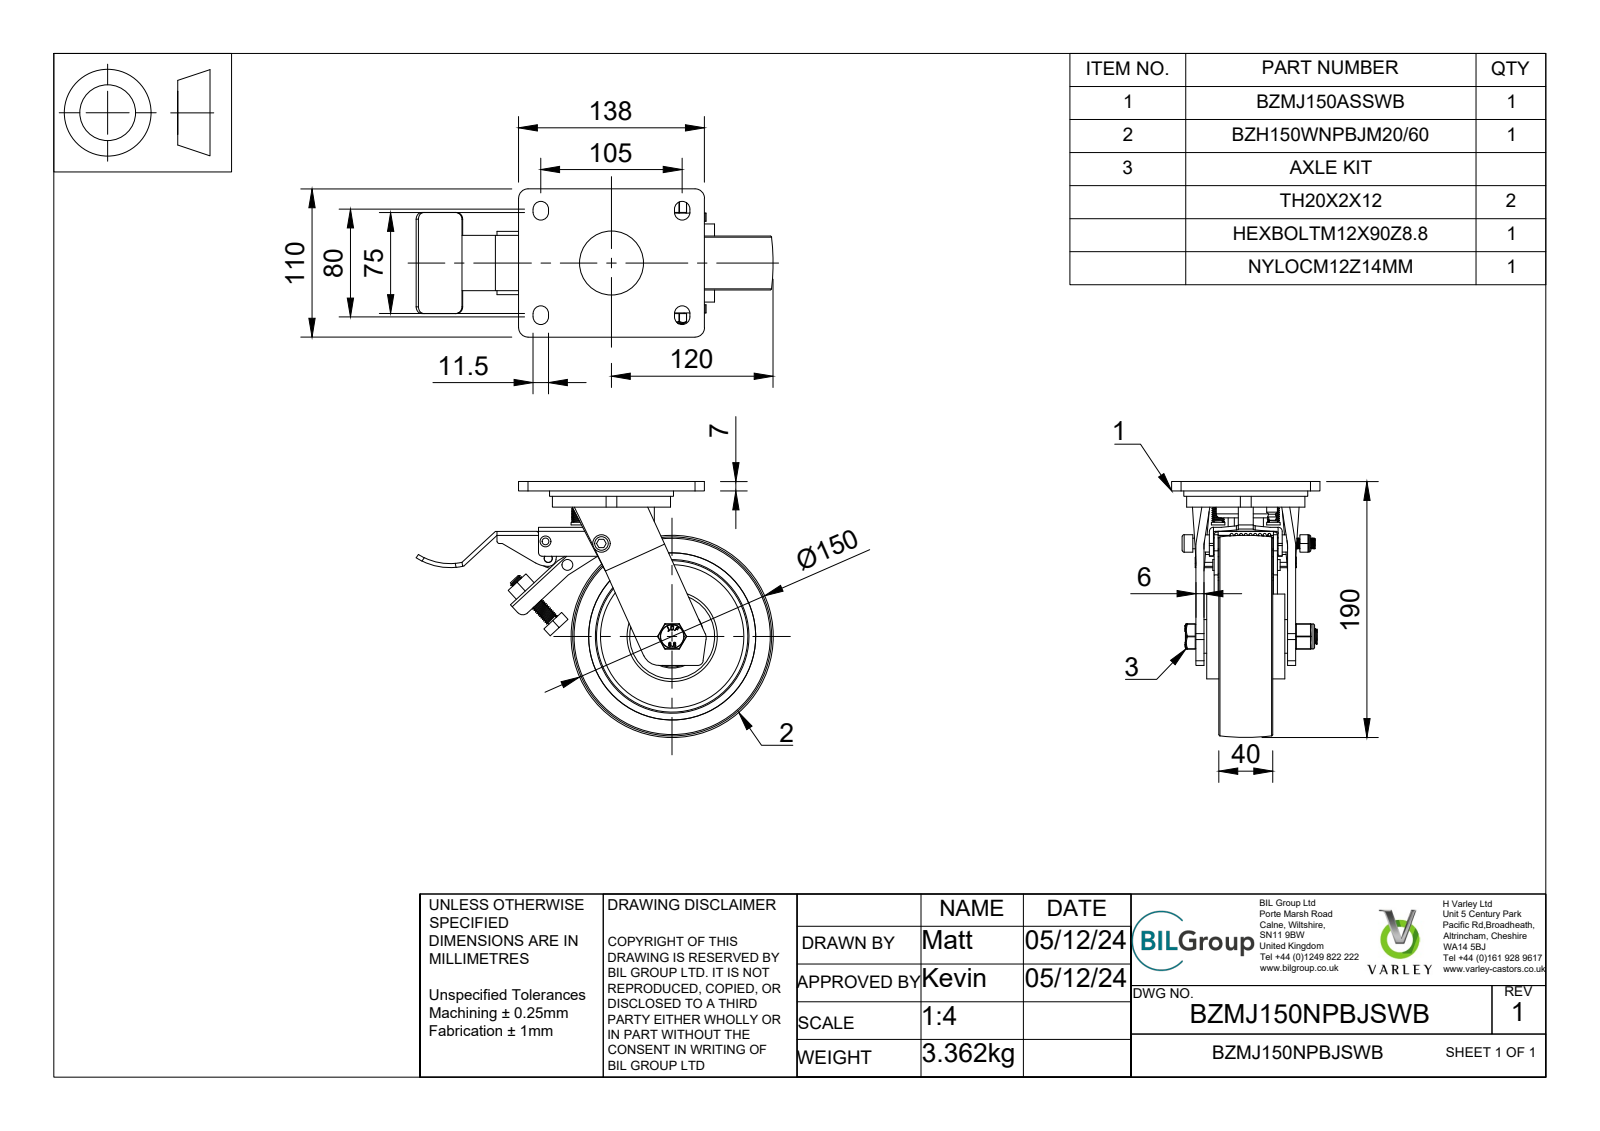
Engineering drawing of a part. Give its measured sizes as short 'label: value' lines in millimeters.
name: BZMJ150NPBJSWB v3; BZH150WNPBJM2060 v1; POLYURETHANE TYRE; NYLON RIM (+7 more)
written by: Autodesk Translation Framework v13.20.0.188 (AP242_MANAGED_MODEL_BASED_3D_ENGINEERING_MIM_LF)
unit: mm
bodies: 60 solids, 1395 faces (599 planar, 363 cylindrical, 433 other)
size: 265 × 190 × 110
volume: 813 848 mm³; area: 303 114 mm²
holes: 3× ⌀6, 1× ⌀8, 1× ⌀8, 1× ⌀10, 1× ⌀12, 1× ⌀12.2, 1× ⌀13, 1× ⌀14, 1× ⌀16, 1× ⌀20, 1× ⌀28.5, 1× ⌀30.8
bosses: 4× ⌀8, 2× ⌀10, 2× ⌀6, 1× ⌀92, 1× ⌀88, 1× ⌀63, 1× ⌀44, 1× ⌀40.8
rounds: 26× R0.5, 8× R5.75, 7× R5, 5× R3, 4× R0.47, 4× R0.9, 4× R1.5, 4× R2
face distances: 5.5, 3, 7, 16.75, 23.25, 17, 11, 27.75, 34.25, 51
hole spacings: 12.83, 15, 23.84, 29.91, 41.05, 41.53, 86.7, 94.15
